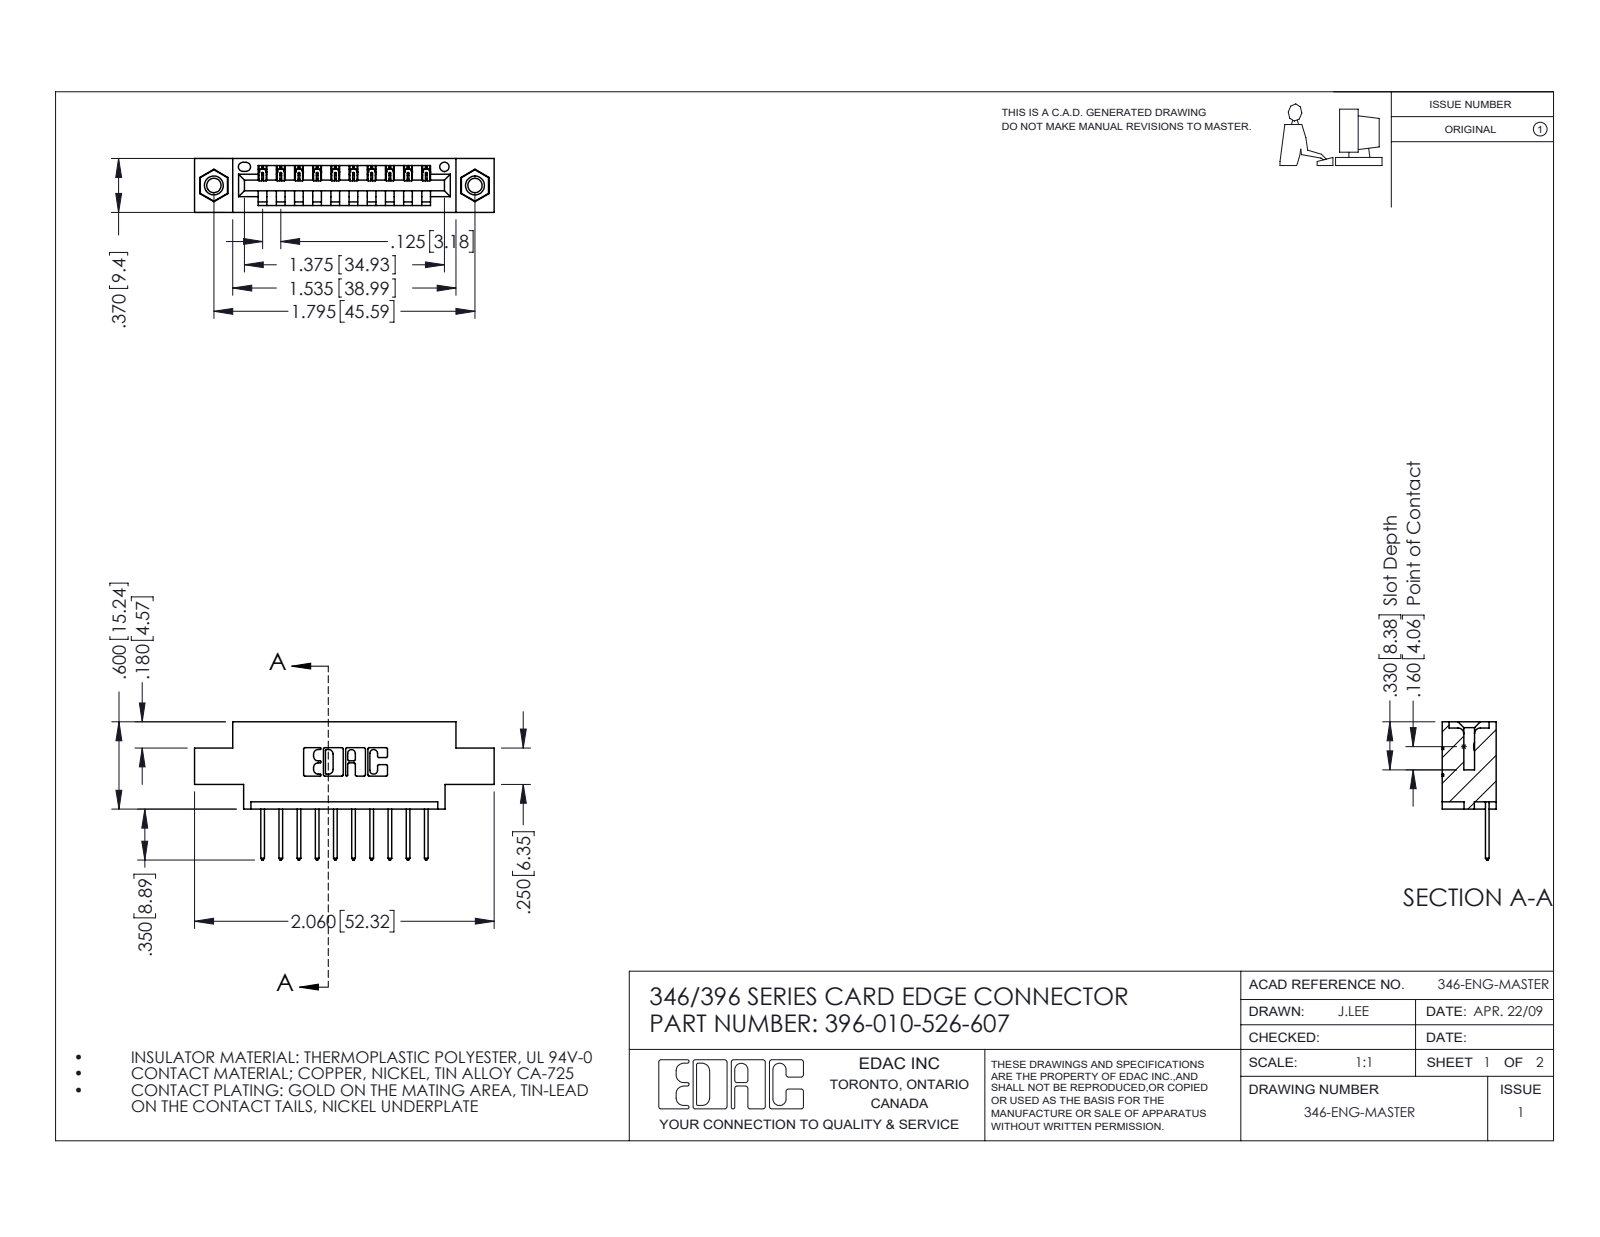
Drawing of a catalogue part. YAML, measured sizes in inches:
part_name: "396-010-526-607; 345-292-001_345-293-126; 345-250-001_345-250-005-103; 346 Part_0.170 Offset - 0.156 Dia-TI"
step_written_by: "SolidWorks 2016 (CONFIG_CONTROL_DESIGN)"
units: inches
bodies: {solids: 13, faces: 766, planar: 512, cylindrical: 238, other: 16}
overall_size: [2.06, 0.95, 0.37]
volume: 0.281
surface_area: 8.687
round_holes:
  - {diameter: 0.098, count: 2}
  - {diameter: 0.125, count: 2}
  - {diameter: 0.156, count: 2}
  - {diameter: 0.064, count: 1}
round_bosses_or_shafts:
  - {diameter: 0.155, count: 2}
partial_cylinders:
  - {radius: 0.01, count: 22}
  - {radius: 0.006, count: 20}
  - {radius: 0.01, count: 20}
  - {radius: 0.007, count: 6}
  - {radius: 0.031, count: 6}
  - {radius: 0.026, count: 3}
  - {radius: 0.031, count: 2}
  - {radius: 0.04, count: 2}
face_to_face_distances: [0.25, 0.37, 0.048, 0.322, 0.222, 0.148, 0.072, 0.298, 0.025, 0.1]
hole_center_spacings: [0.246, 1.59, 1.795]
